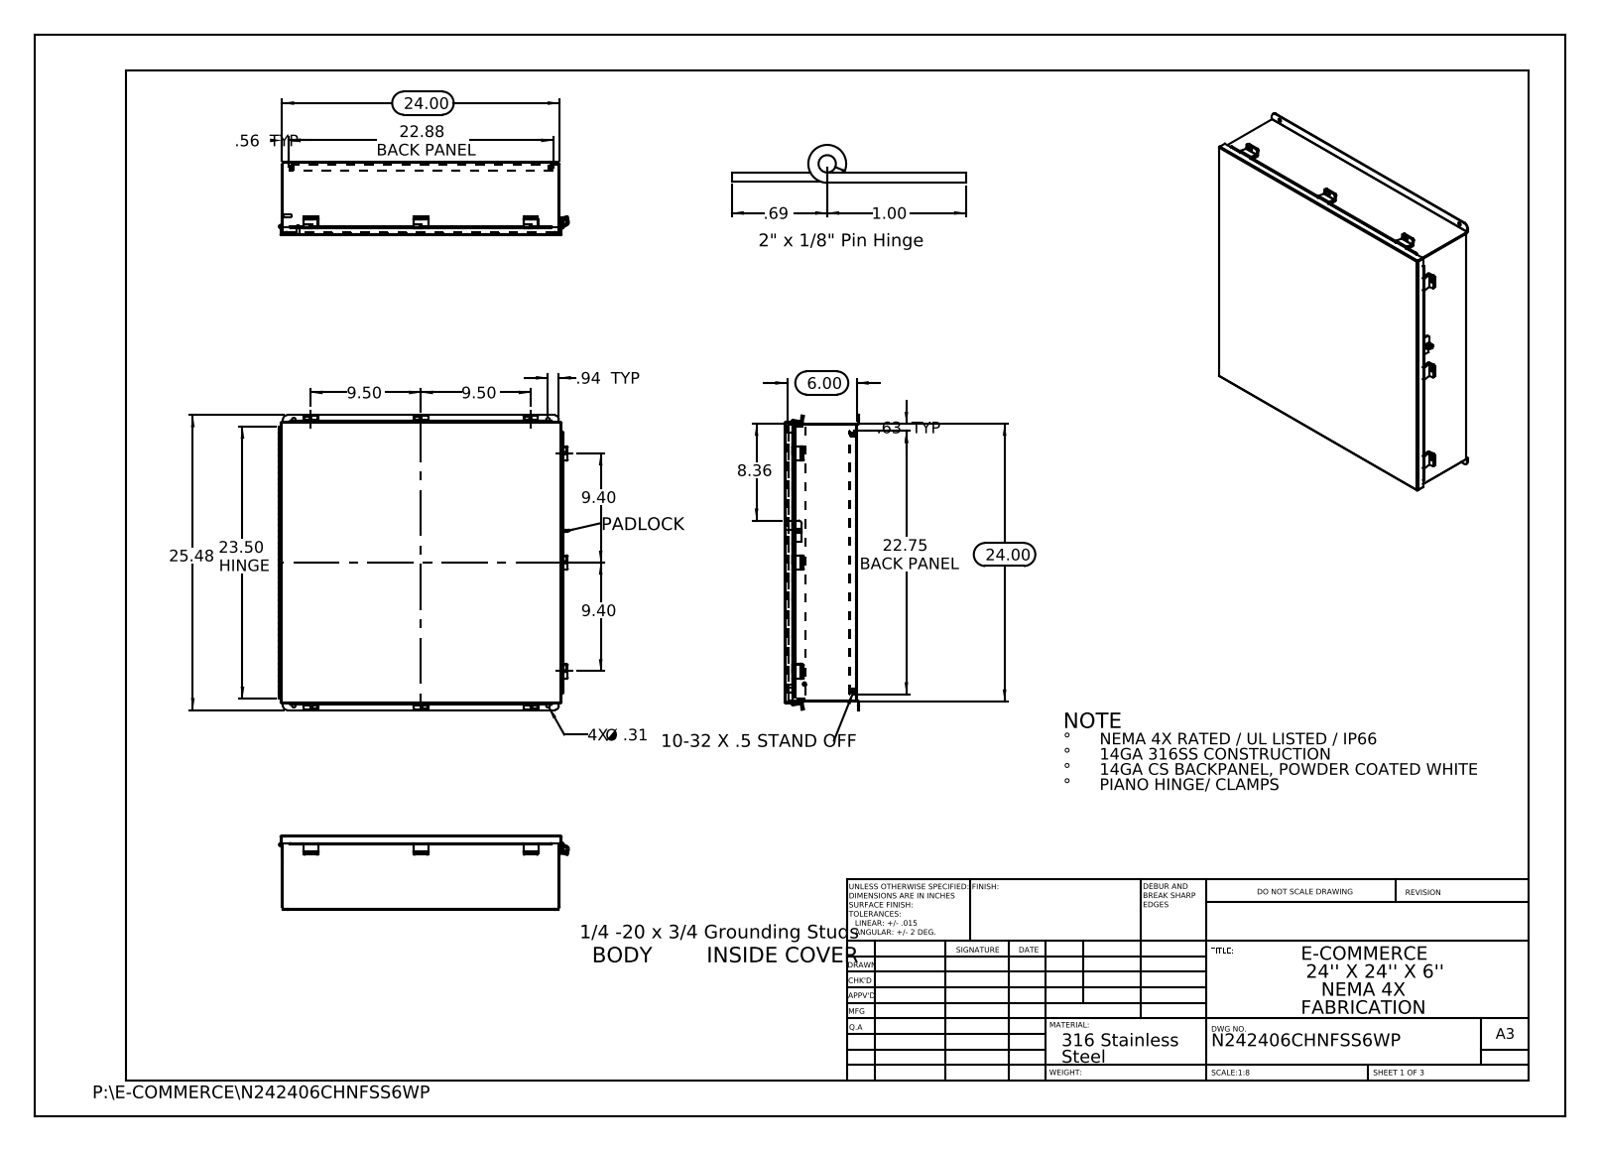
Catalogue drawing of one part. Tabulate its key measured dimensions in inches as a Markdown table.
| quantity | value |
| --- | --- |
| part name | N242406CHNFSS6WP JIC Clamp Bracket; N242406CHNFSS6WP JIC Bottom; N242406CHNFSS6WP Hinge Body Side; N242406CHNFSS6WP HW-CD-S-25020-034 (+8 more) |
| STEP written by | SolidWorks 2013 (CONFIG_CONTROL_DESIGN) |
| units | inches |
| bodies | 33 solids, 1148 faces (715 planar, 413 cylindrical, 20 other) |
| overall size | 25.476 × 25.072 × 6.39 |
| volume | 184.4 in³ |
| surface area | 4 990 in² |
| round holes (diameter × count) | 0.25 × 13, 0.187 × 4, 0.312 × 4, 0.125 × 1, 0.125 × 1, 0.373 × 1, 0.375 × 1 |
| round bosses / shafts (diameter × count) | 0.313 × 4, 0.315 × 2, 0.236 × 2, 0.273 × 1, 0.25 × 1 |
| partial cylindrical surfaces (radius × count) | 0.125 × 31, 0.133 × 18, 0.013 × 13, 0.009 × 12, 0.088 × 12, 0.083 × 6, 0.1 × 6, 0.375 × 4 |
| main face-to-face distances | 0.075, 6.128, 23.925, 6.053, 6.203, 0.074, 5.628, 0.575, 0.5, 5.553 |
| hole center spacings | 1.315, 9.5, 22.213, 23.427, 32.257, 9.425, 19, 21.976 |
